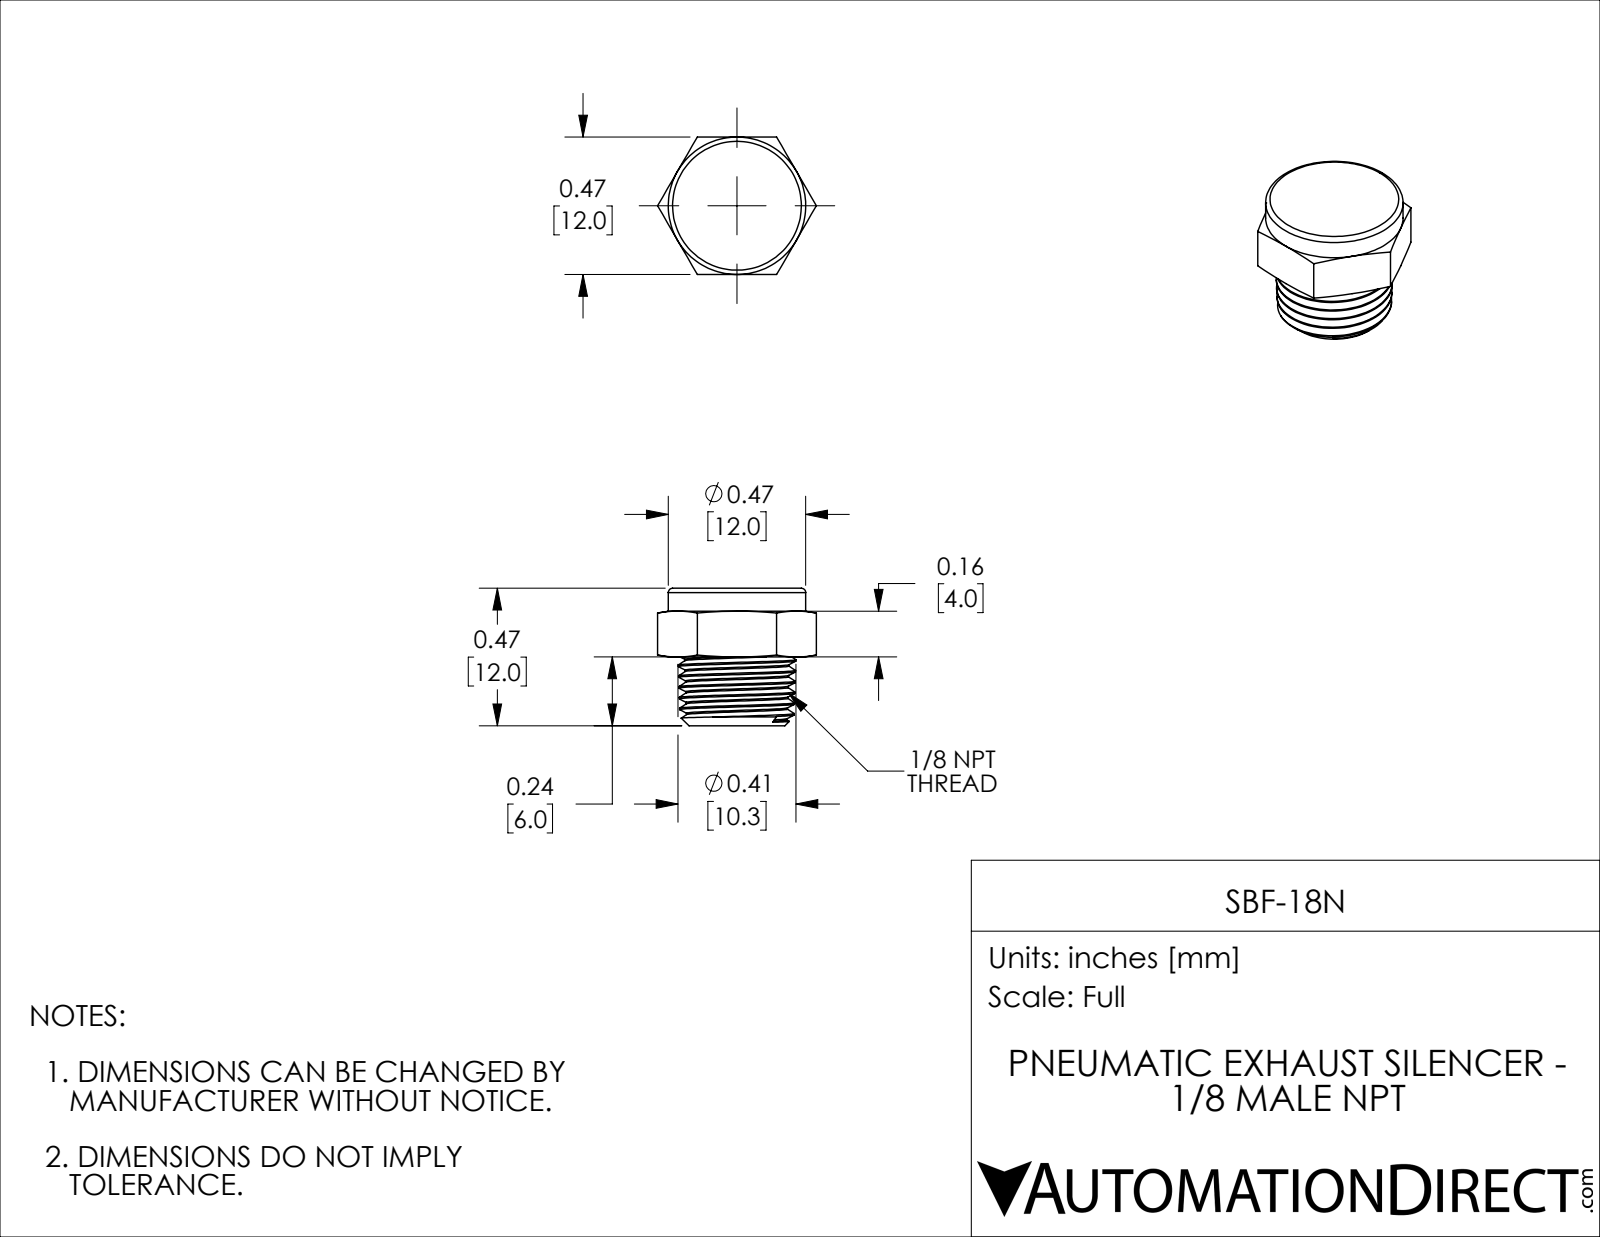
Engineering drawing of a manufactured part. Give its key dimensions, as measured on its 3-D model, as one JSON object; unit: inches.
{"part_name": "SBF-18N", "step_written_by": "SolidWorks 2021 (CONFIG_CONTROL_DESIGN)", "units": "inches", "bodies": {"solids": 1, "faces": 47, "planar": 11, "cylindrical": 4, "other": 32}, "overall_size": [0.546, 0.472, 0.472], "volume_in3": 0.041, "surface_area_in2": 1.557, "round_holes": [[0.314, 1]], "round_bosses_or_shafts": [[0.472, 1]], "face_to_face_distances": [0.472, 0.097, 0.236, 0.139, 0.375]}
